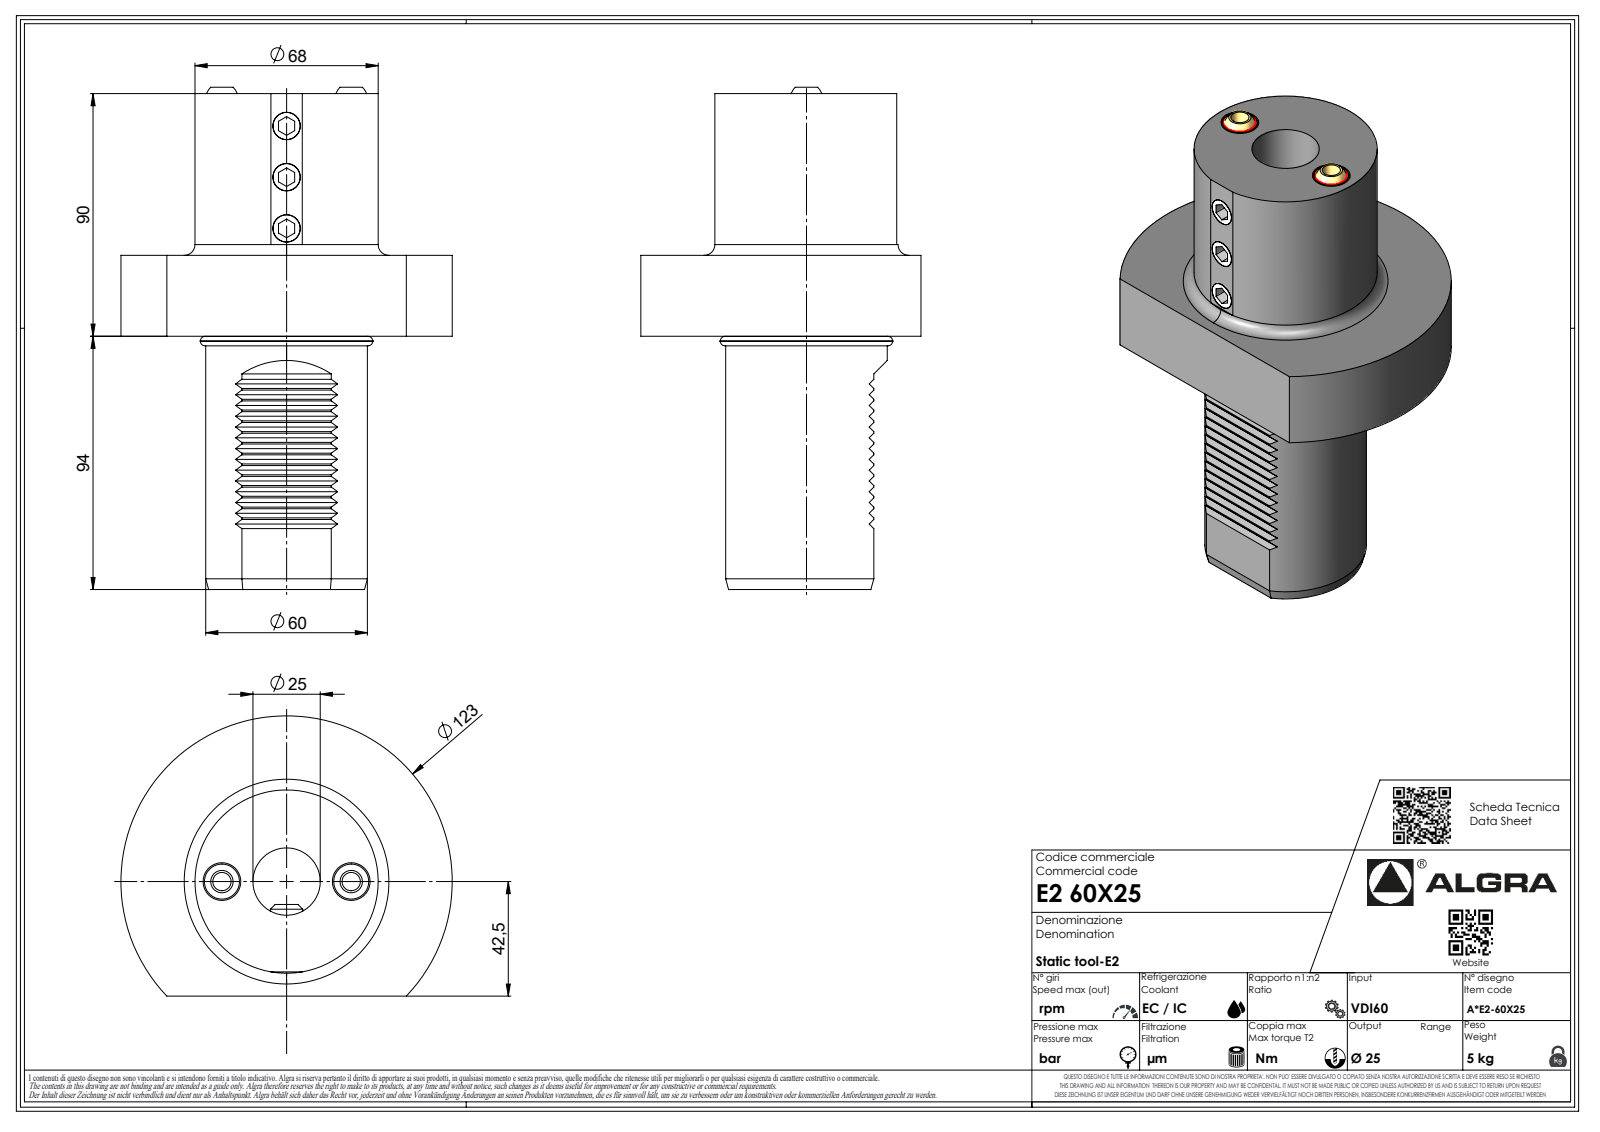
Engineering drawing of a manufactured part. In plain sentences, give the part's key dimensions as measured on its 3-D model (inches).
The part is named "E260X25". Its 3-D file was written by "SolidWorks 2023 (AUTOMOTIVE_DESIGN)". It is 1 solid with 283 faces: 201 planar, 33 cylindrical and 49 other. Overall it measures 7.337 by 4.843 by 4.094 inches. Its volume is 46.04 cubic inches and its surface area 109.4 square inches. Round holes: 1 of diameter 0.083, 1 of diameter 0.984. Round bosses or shafts: 1 of diameter 2.677, 1 of diameter 2.527, 1 of diameter 2.362, 1 of diameter 0.251, 1 of diameter 0.067. Partial cylindrical surfaces (rounded edges, fillets, slot ends): 7 of radius 0.013, 7 of radius 0.02, 7 of radius 0.146, 1 of radius 0.008, 1 of radius 2.421. The main face-to-face distances are 1.181, 2.362, 3.543, 7.244, 4.882, 3.701, 0.111, 0.557, 0.445, 0.223.
